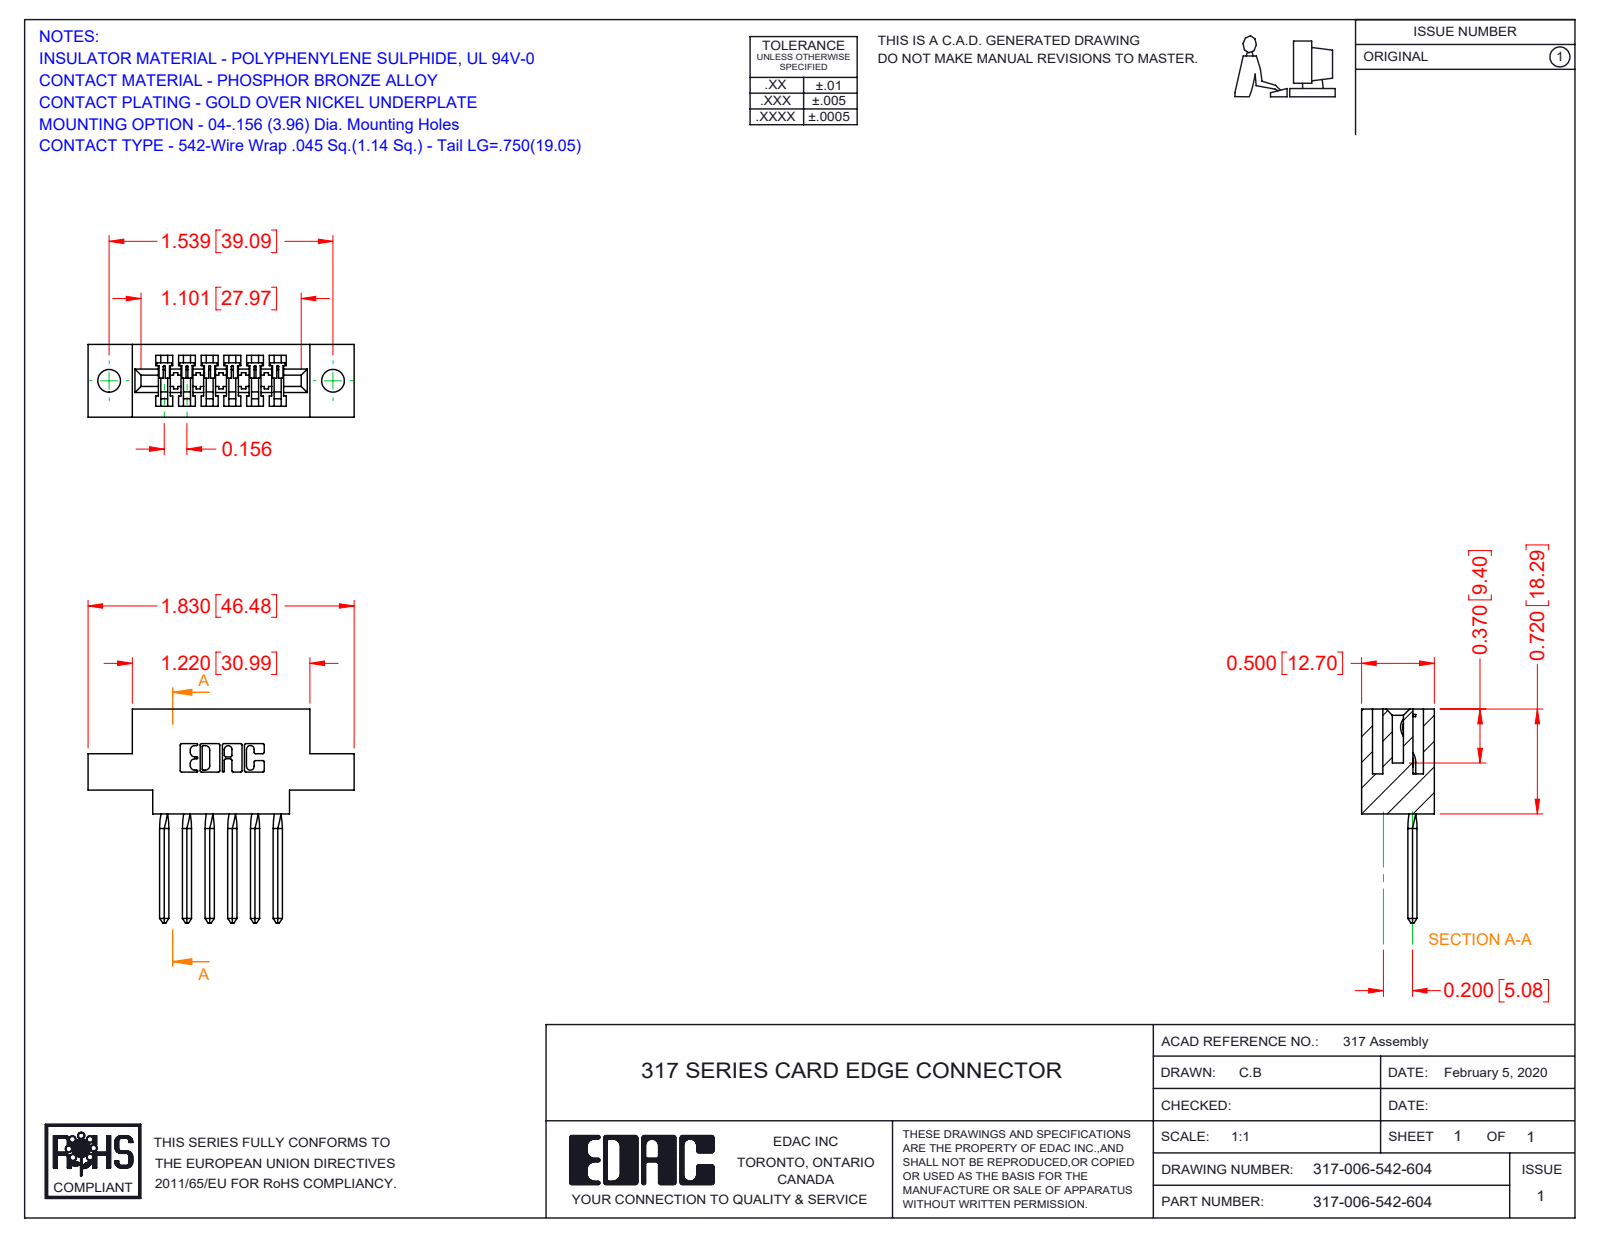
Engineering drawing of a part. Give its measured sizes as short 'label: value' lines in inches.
name: 317-290-003_542; 317-006-542-604; 317 Part_.156 Dia - TH
written by: SolidWorks 2016 (CONFIG_CONTROL_DESIGN)
unit: in
bodies: 7 solids, 552 faces (442 planar, 86 cylindrical, 24 other)
size: 1.83 × 1.47 × 0.5
volume: 0.374 in³; area: 10.05 in²
holes: 2× ⌀0.156
rounds: 22× R0.01, 12× R0.006, 6× R0.007, 6× R0.031, 3× R0.026, 1× R0.074, 1× R0.089, 1× R0.1
face distances: 0.5, 0.075, 0.425, 0.156, 0.11, 0.065, 0.116, 0.163, 0.136, 0.305
hole spacings: 1.539
